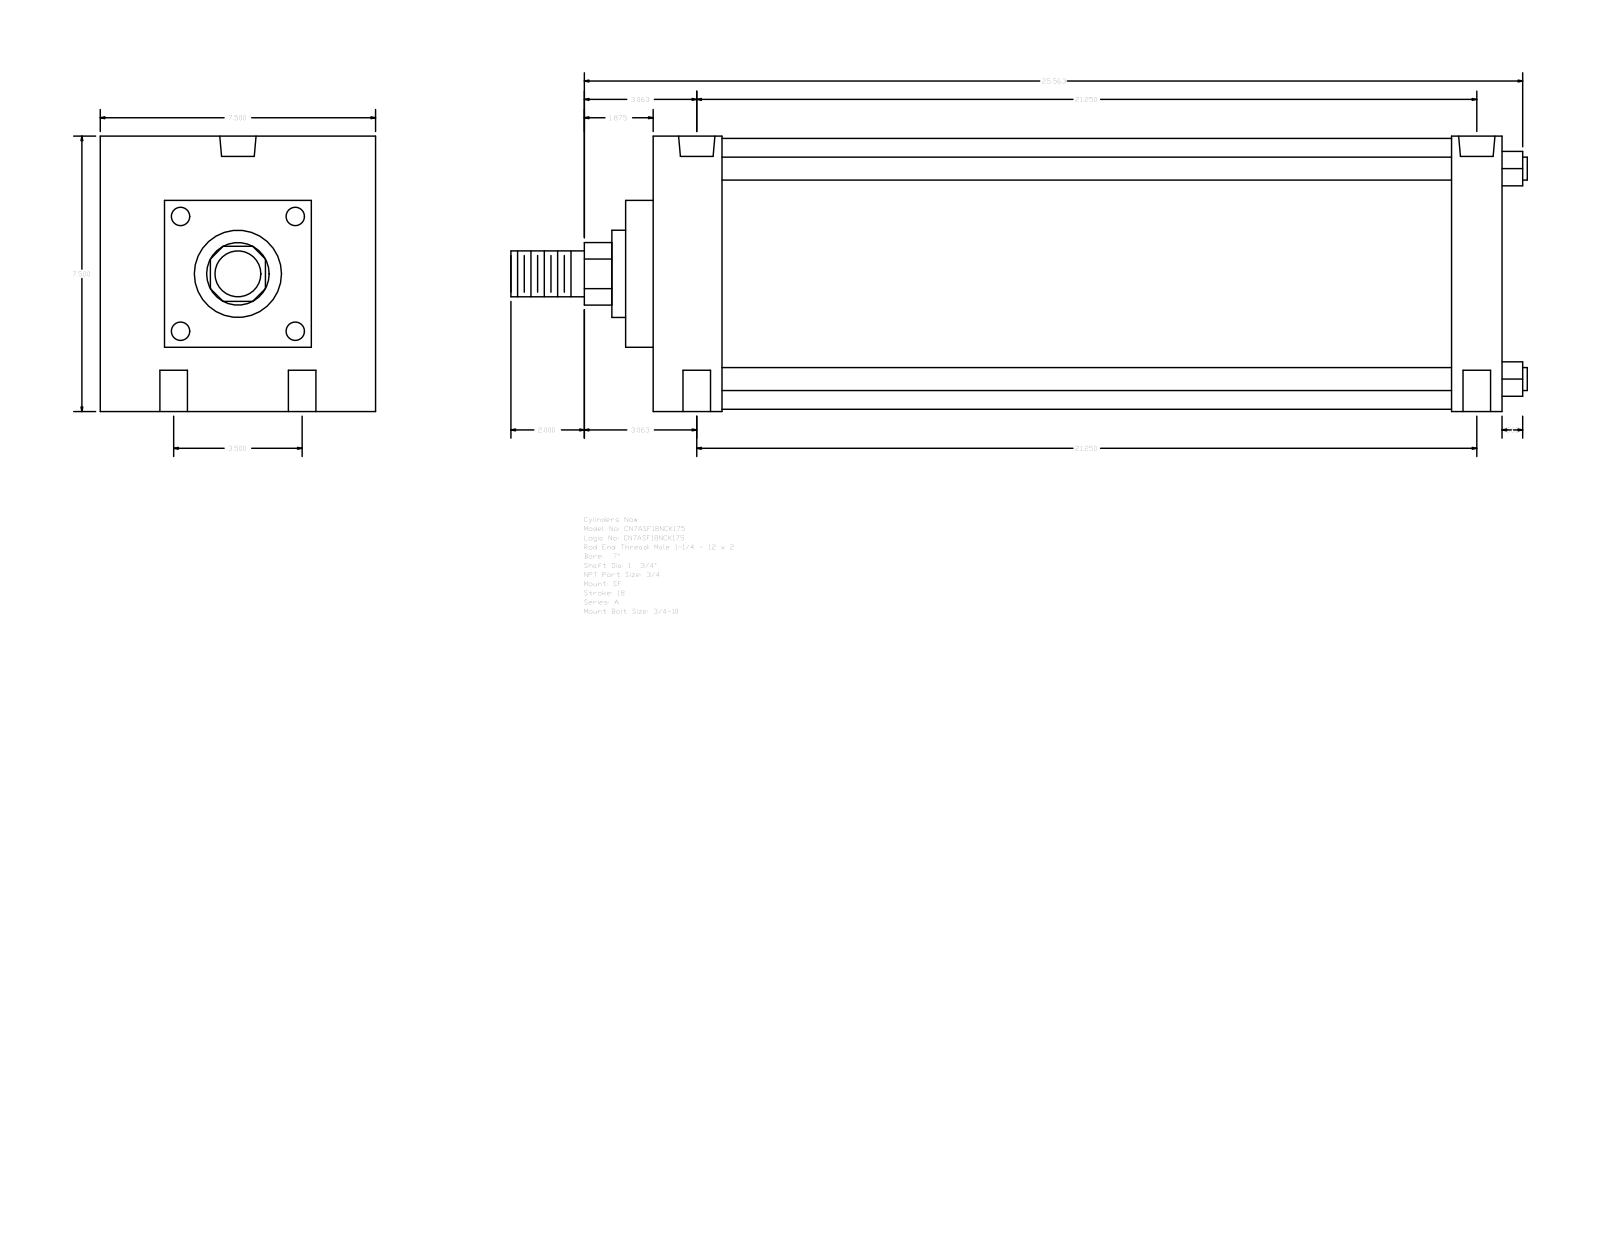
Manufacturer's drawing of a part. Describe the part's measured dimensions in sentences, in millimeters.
The part is named "A_SF__0700_1.75". Its 3-D file was written by "GSSL Pune (CONFIG_CONTROL_DESIGN)". It is 0 solids with 93 faces: 67 planar, 26 cylindrical and 0 other. Overall it measures 703.26 by 190.5 by 190.5 millimeters. Round holes: 4 of diameter 19.05, 2 of diameter 15.08, 2 of diameter 25.12. Round bosses or shafts: 4 of diameter 15.88, 1 of diameter 187.32, 1 of diameter 60.33, 1 of diameter 44.45, 1 of diameter 31.75. Partial cylindrical surfaces (rounded edges, fillets, slot ends): 1 of radius 21.63. The main face-to-face distances are 190.5, 587.38, 146.05, 19.05, 47.63, 552.46, 504.83, 539.75, 34.92, 44.45. The hole center spacings are 44.45, 541.58, 539.75, 88.9, 547.02, 528.63.
